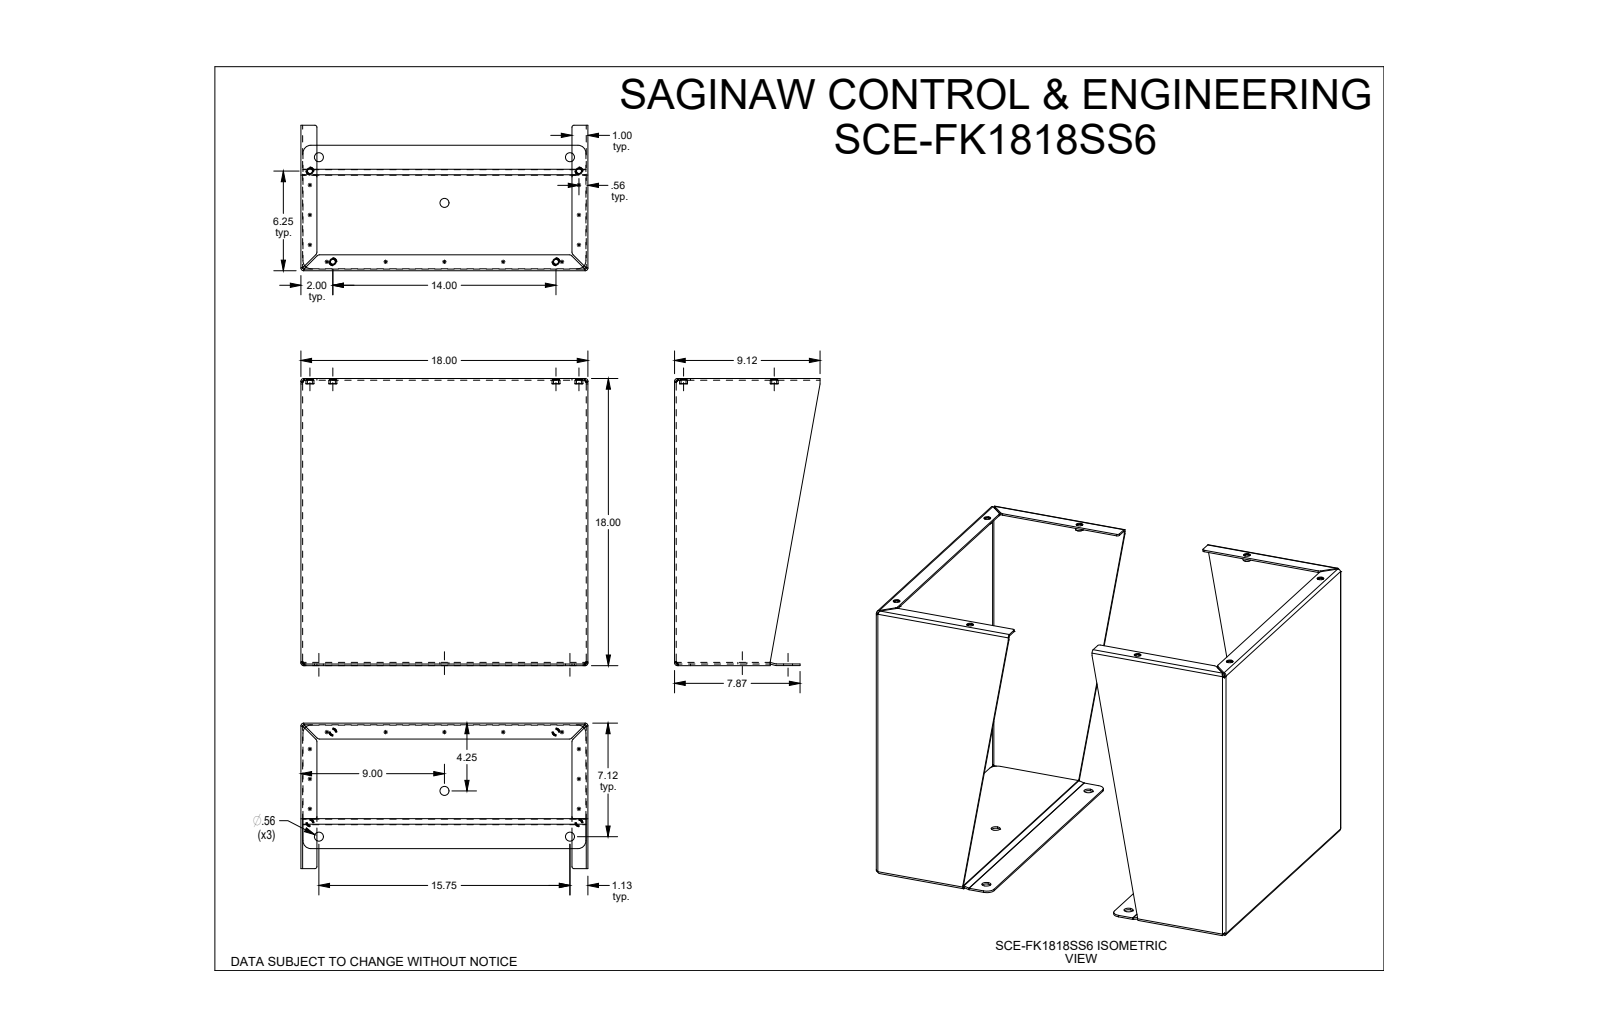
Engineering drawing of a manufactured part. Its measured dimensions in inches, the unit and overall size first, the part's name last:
Units: inches
Overall size (bounding box): 24 × 18 × 18
Round holes (diameter × count): ⌀0.312 ×8, ⌀0.413 ×8, ⌀0.563 ×6
Round bosses / shafts (diameter × count): ⌀0.5 ×8, ⌀0.412 ×8
Partial cylindrical surfaces — rounded edges, fillets, slot ends (radius × count): R0.166 ×16, R0.062 ×12, R0.125 ×8, R0.22 ×8, R0.5 ×8, R0.063 ×6
Main face-to-face distances: 0.104, 23.896, 17.896, 17.792, 24, 23.792, 18, 0.101, 17.893, 17.688
Hole centre spacings: 1.035, 5.866, 6.614, 7.913, 8.671, 10.646, 14.884, 15.919
Volume: 162.2 in³ · Surface area: 3 157 in²
Bodies: 12 solids, 286 faces (120 planar, 110 cylindrical, 56 other)
Part name (STEP PRODUCT): SCE-FK1818SS6
STEP written by: SolidWorks 2019 (CONFIG_CONTROL_DESIGN)
